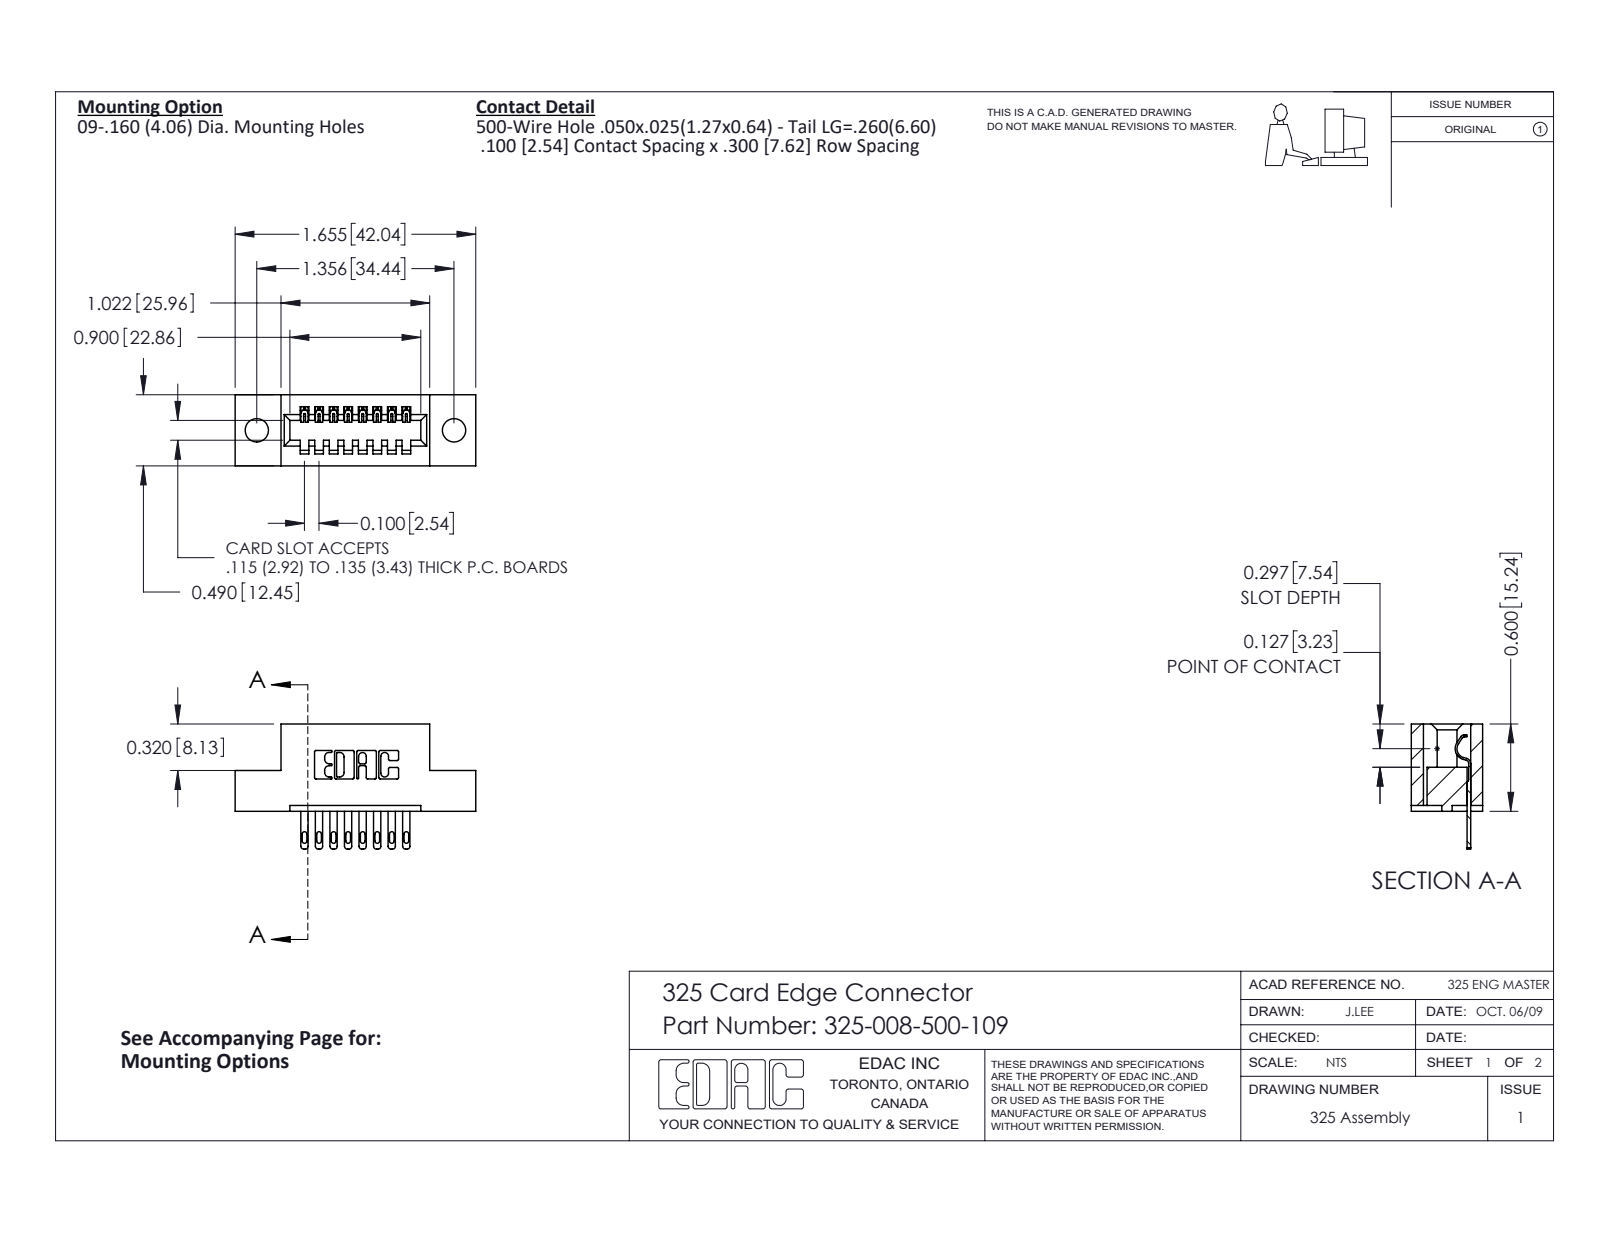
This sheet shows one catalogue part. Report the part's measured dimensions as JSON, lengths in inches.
{"part_name": "325-292-001_325-293-100; 325-008-500-109; 325 Part_.160 TH", "step_written_by": "SolidWorks 2016 (CONFIG_CONTROL_DESIGN)", "units": "inches", "bodies": {"solids": 9, "faces": 546, "planar": 358, "cylindrical": 188, "other": 0}, "overall_size": [1.655, 0.86, 0.49], "volume_in3": 0.296, "surface_area_in2": 7.175, "round_holes": [[0.16, 2]], "partial_cylinders_radius": [[0.01, 22], [0.006, 16], [0.016, 16], [0.02, 16], [0.007, 6], [0.031, 6], [0.026, 3], [0.014, 1]], "face_to_face_distances": [0.3, 0.1, 0.2, 0.04, 0.083, 0.407, 0.49, 0.4, 0.06, 0.6], "hole_center_spacings": [1.356]}
